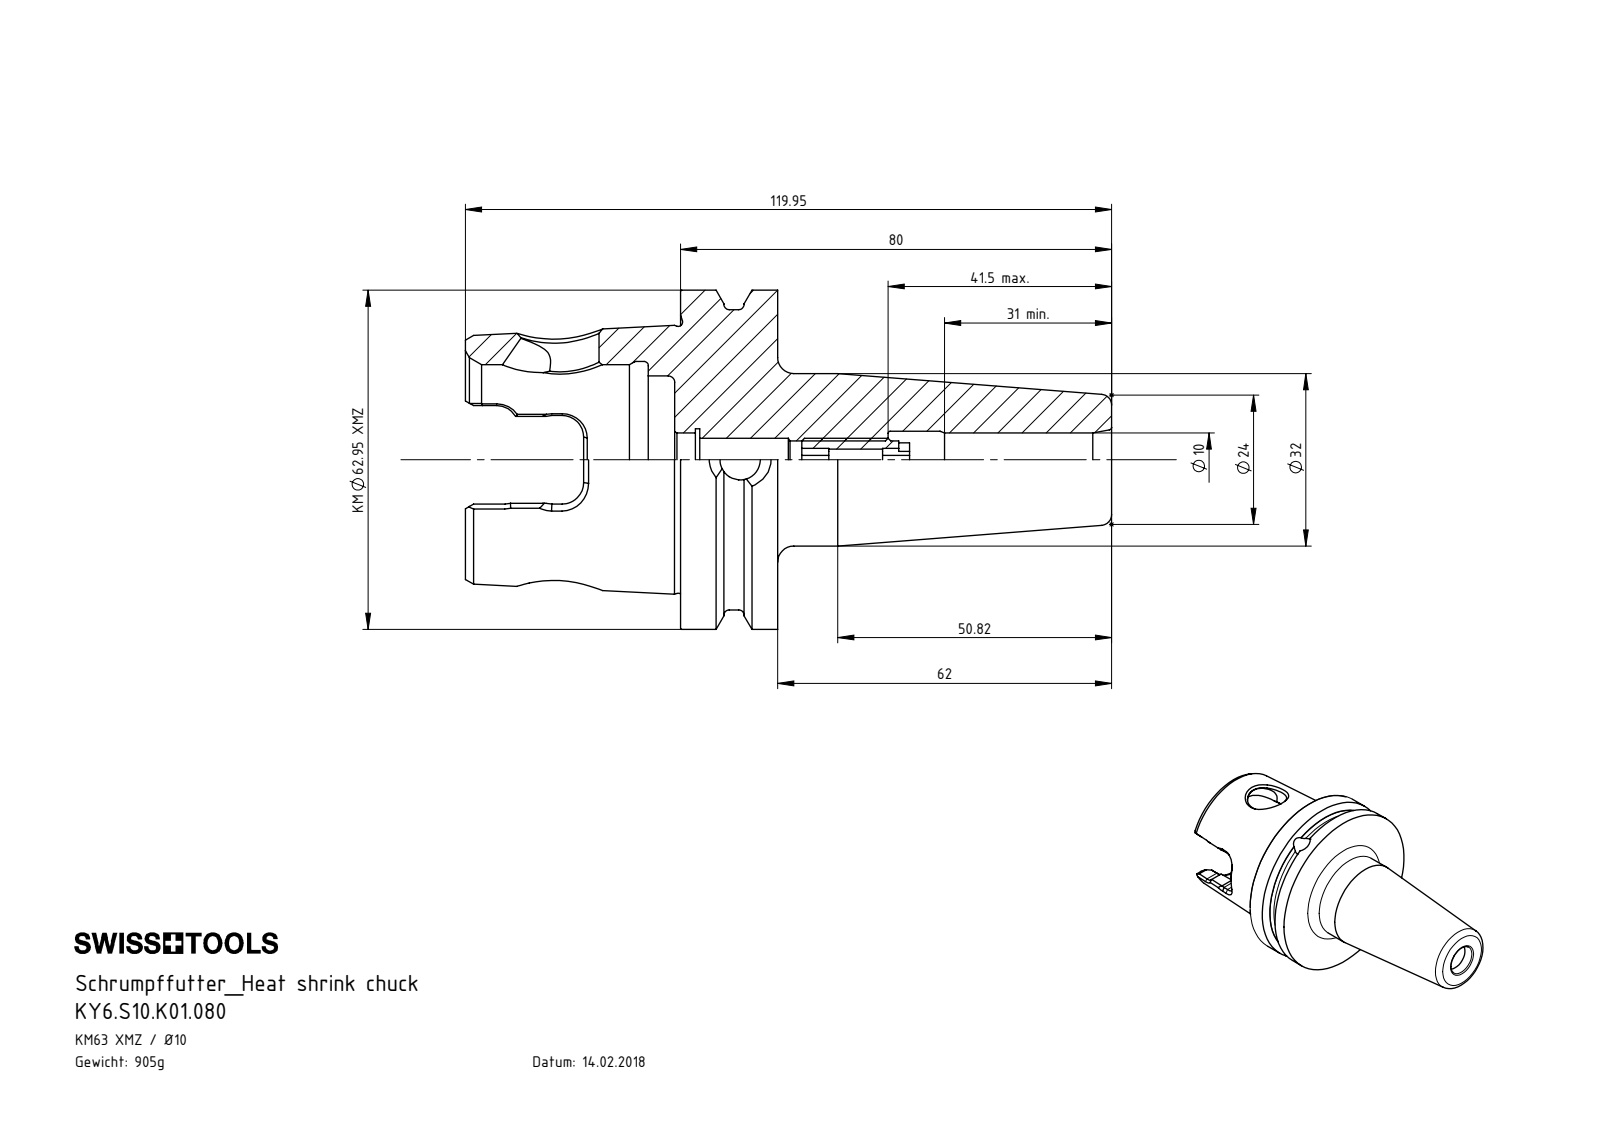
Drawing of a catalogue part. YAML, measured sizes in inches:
part_name: "KY6-S10.K01.080; ERU-AN3.K01.020_A; KY6-S10.K01.080_A"
step_written_by: "SolidWorks 2012 (CONFIG_CONTROL_DESIGN)"
units: inches
bodies: {solids: 2, faces: 272, planar: 79, cylindrical: 60, other: 133}
overall_size: [4.722, 2.478, 2.478]
volume: 7.037
surface_area: 43.13
round_holes:
  - {diameter: 0.294, count: 2}
  - {diameter: 0.157, count: 1}
  - {diameter: 0.276, count: 1}
  - {diameter: 0.315, count: 1}
  - {diameter: 0.334, count: 1}
  - {diameter: 0.394, count: 1}
  - {diameter: 0.417, count: 1}
  - {diameter: 0.453, count: 1}
  - {diameter: 0.571, count: 1}
  - {diameter: 1.224, count: 1}
  - {diameter: 1.389, count: 1}
  - {diameter: 1.437, count: 1}
round_bosses_or_shafts:
  - {diameter: 2.478, count: 1}
  - {diameter: 2.193, count: 1}
  - {diameter: 1.26, count: 1}
partial_cylinders:
  - {radius: 0.157, count: 6}
  - {radius: 0.277, count: 2}
face_to_face_distances: [0.709, 0.043, 0.752, 3.193, 3.15, 2.441, 0.193, 0.236, 0.945, 3.386]
